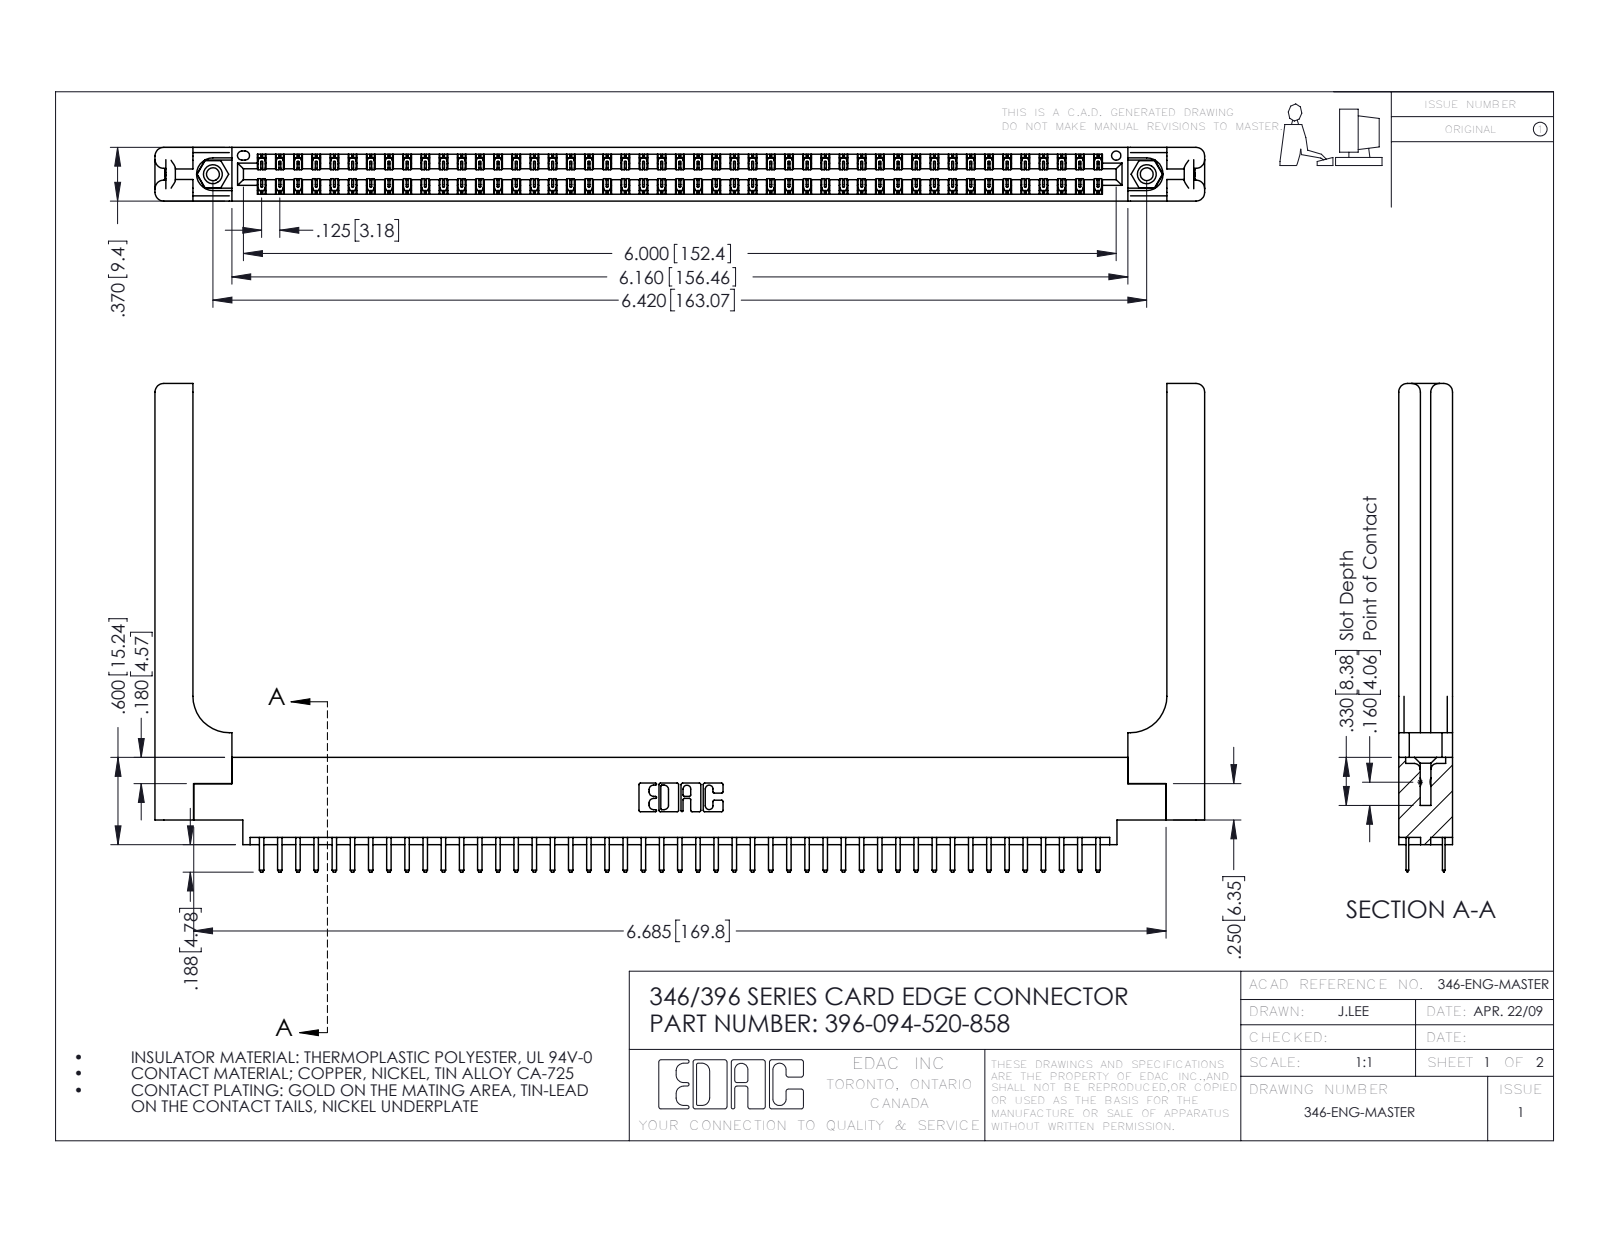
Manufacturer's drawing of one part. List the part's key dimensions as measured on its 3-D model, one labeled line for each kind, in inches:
Part name (STEP PRODUCT): 396-094-520-858; 346 Part_0.170 Offset - 0.156 Dia-TH; 346-220-058_345-220-058; 345-250-001_345-250-001-102 (+1 more)
STEP written by: SolidWorks 2016 (CONFIG_CONTROL_DESIGN)
Units: inches
Bodies: 99 solids, 5646 faces (3706 planar, 1880 cylindrical, 60 other)
Overall size (bounding box): 7.216 × 3.358 × 0.37
Volume: 1.538 in³ · Surface area: 45.7 in²
Round holes (diameter × count): ⌀0.089 ×2, ⌀0.125 ×2, ⌀0.156 ×2, ⌀0.064 ×1
Round bosses / shafts (diameter × count): ⌀0.155 ×2
Partial cylindrical surfaces — rounded edges, fillets, slot ends (radius × count): R0.006 ×141, R0.01 ×98, R0.01 ×22, R0.06 ×16, R0.007 ×6, R0.031 ×6, R0.026 ×3, R0.014 ×2
Main face-to-face distances: 0.37, 0.048, 0.322, 0.072, 0.25, 0.148, 0.15, 0.298, 0.025, 0.275
Hole centre spacings: 0.246, 6.211, 6.42
